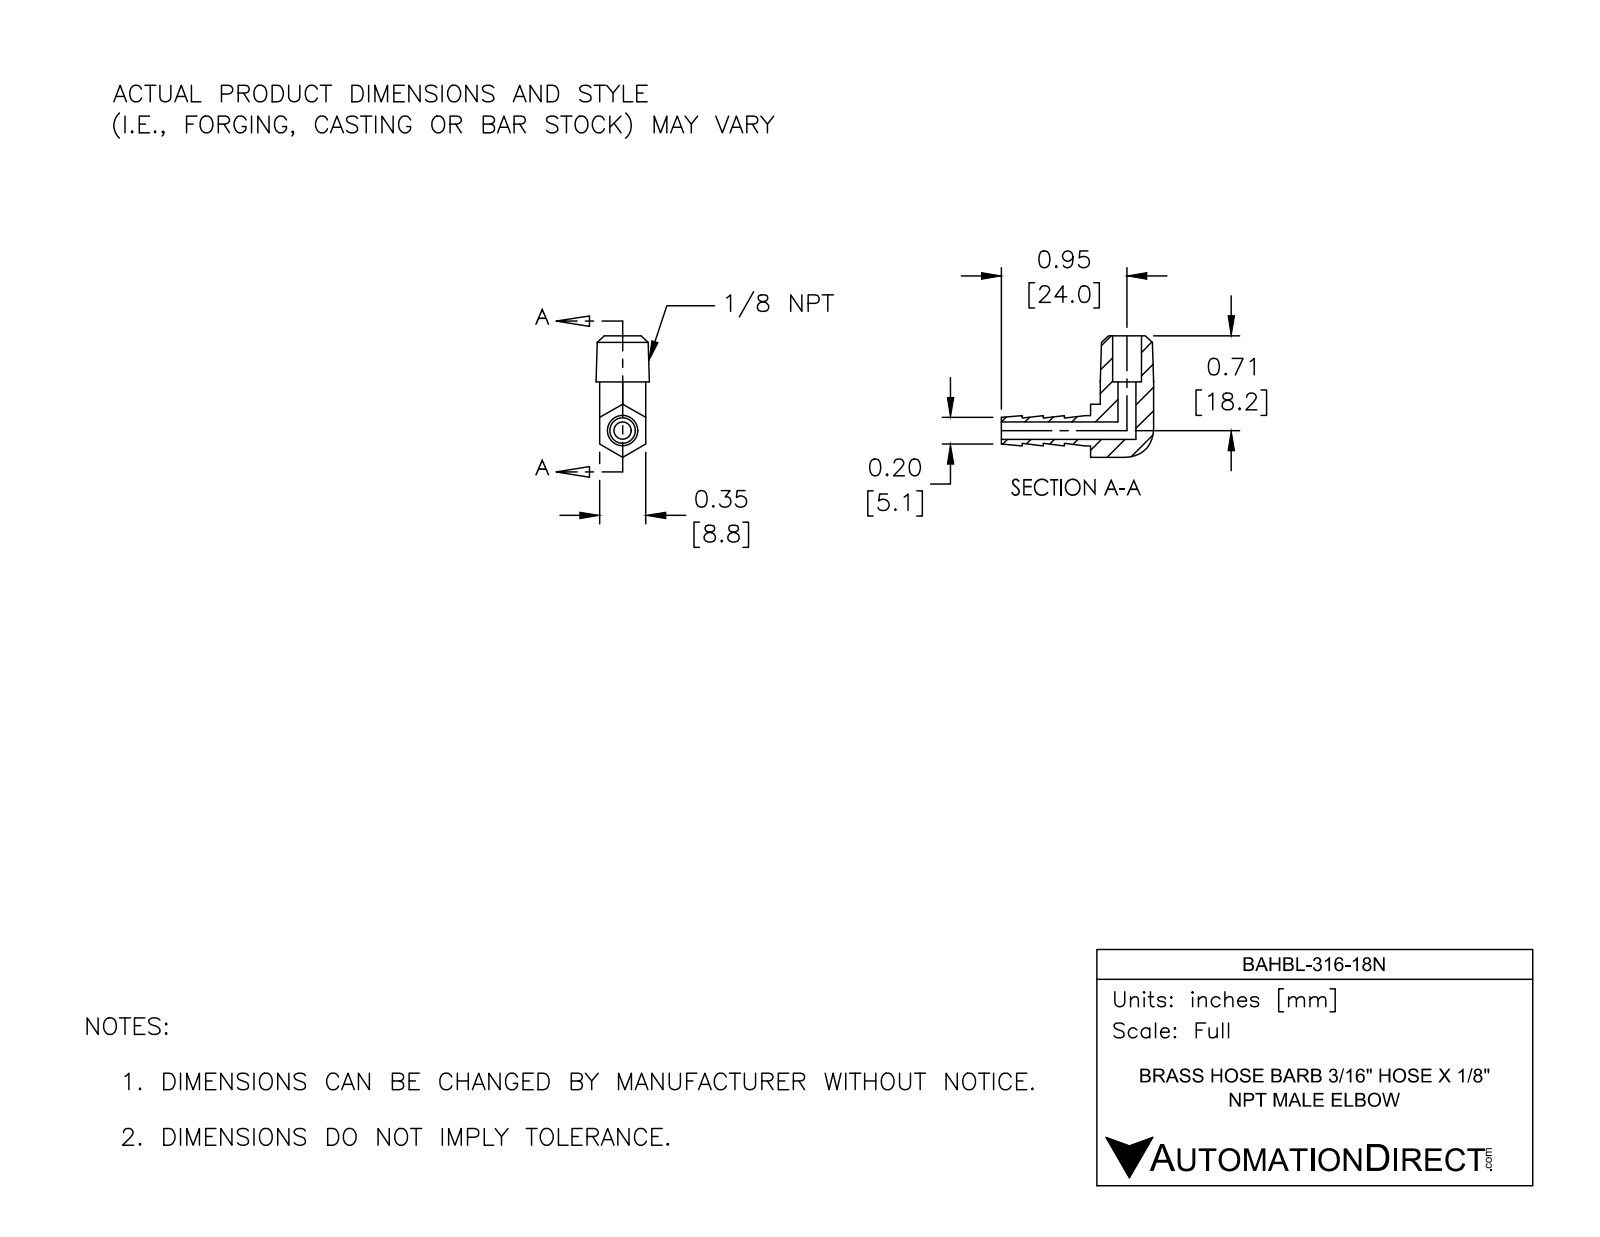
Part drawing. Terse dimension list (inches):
name: BAHBL-316-18N
written by: SolidWorks 2017 (AUTOMOTIVE_DESIGN)
unit: in
bodies: 1 solid, 41 faces (19 planar, 10 cylindrical, 12 other)
size: 1.146 × 0.915 × 0.401
volume: 0.096 in³; area: 2.587 in²
holes: 1× ⌀0.131, 1× ⌀0.136, 1× ⌀0.217
bosses: 1× ⌀0.227
rounds: 2× R0.25
face distances: 0.347, 0.347, 0.158, 0.316, 0.348, 0.671, 0.432, 0.78, 0.197, 0.355
